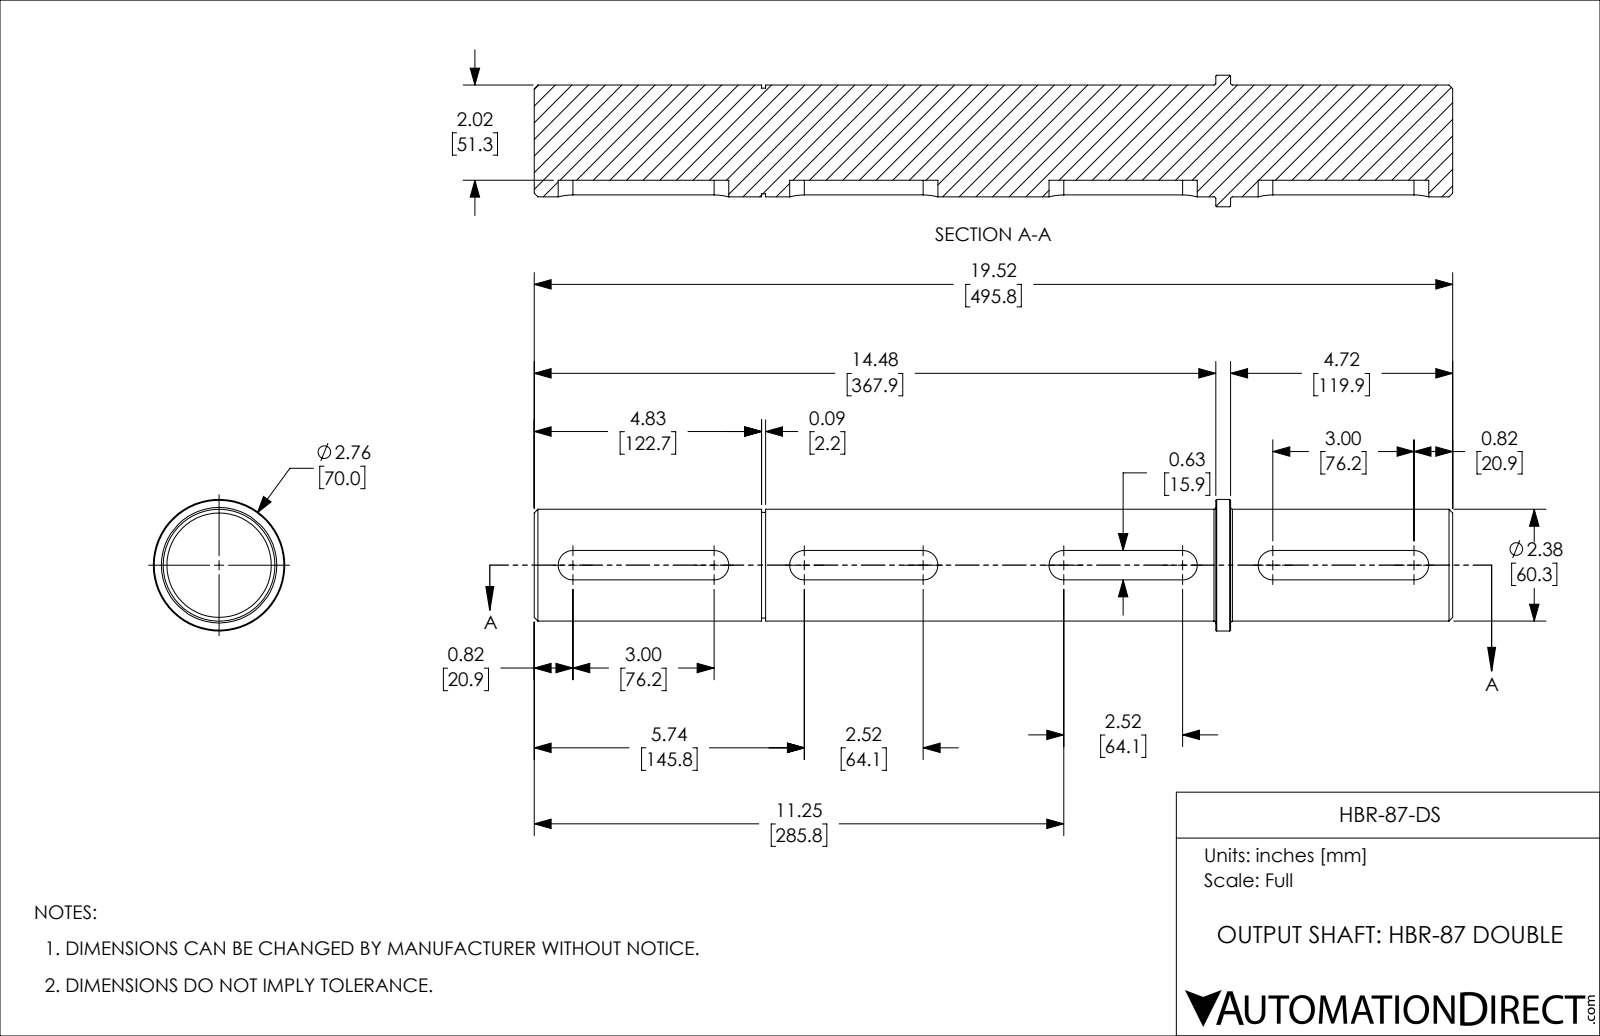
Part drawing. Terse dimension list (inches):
name: HBR-87-DS
written by: SolidWorks 2018 (AUTOMOTIVE_DESIGN)
unit: in
bodies: 1 solid, 52 faces (18 planar, 22 cylindrical, 12 other)
size: 19.519 × 2.795 × 2.795
volume: 84.15 in³; area: 167.5 in²
bosses: 1× ⌀2.795, 1× ⌀2.375, 1× ⌀2.244
rounds: 5× R0.312, 3× R0.313
face distances: 19.519, 0.625, 14.484, 5.035, 14.799, 0.315, 4.72, 4.917, 9.567, 9.882
